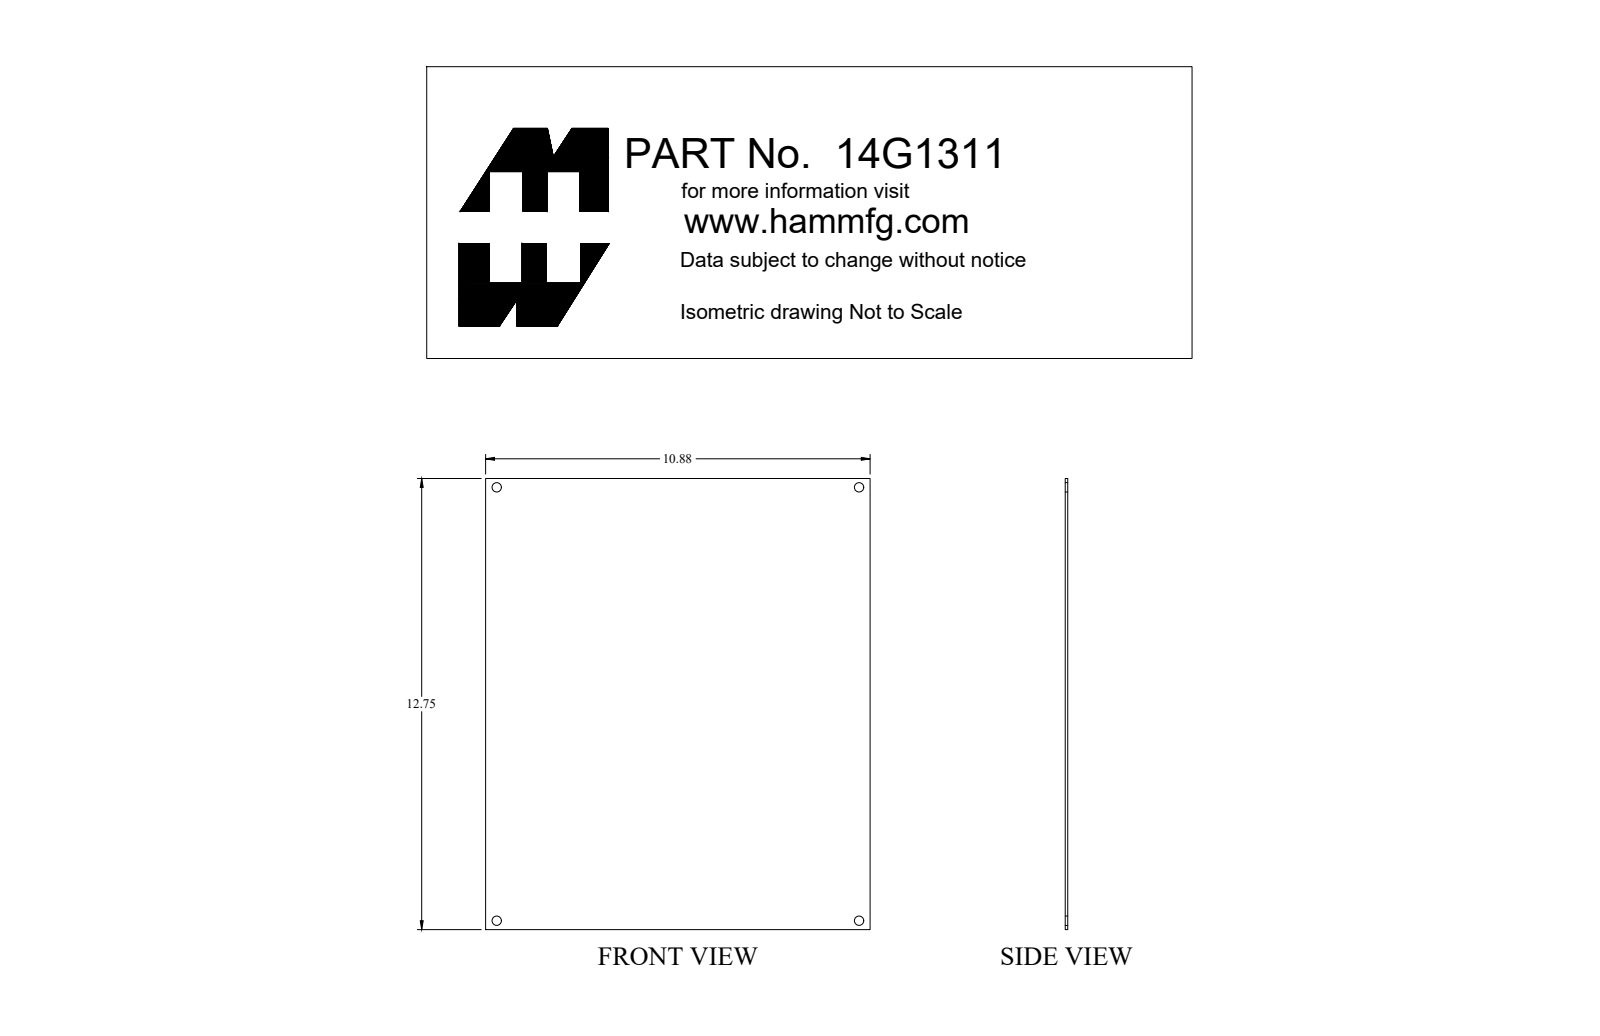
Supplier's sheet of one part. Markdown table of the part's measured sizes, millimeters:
| quantity | value |
| --- | --- |
| part name | 14G1311 |
| STEP written by | SolidWorks 2018 (AUTOMOTIVE_DESIGN) |
| units | millimeters |
| bodies | 1 solid, 10 faces (6 planar, 4 cylindrical, 0 other) |
| overall size | 323.9 × 276.2 × 1.8 |
| volume | 163 300 mm³ |
| surface area | 181 000 mm² |
| round holes (diameter × count) | 6.7 × 4 |
| main face-to-face distances | 1.8, 276.2, 323.9 |
| hole center spacings | 260.4, 311.2, 405.7 |
